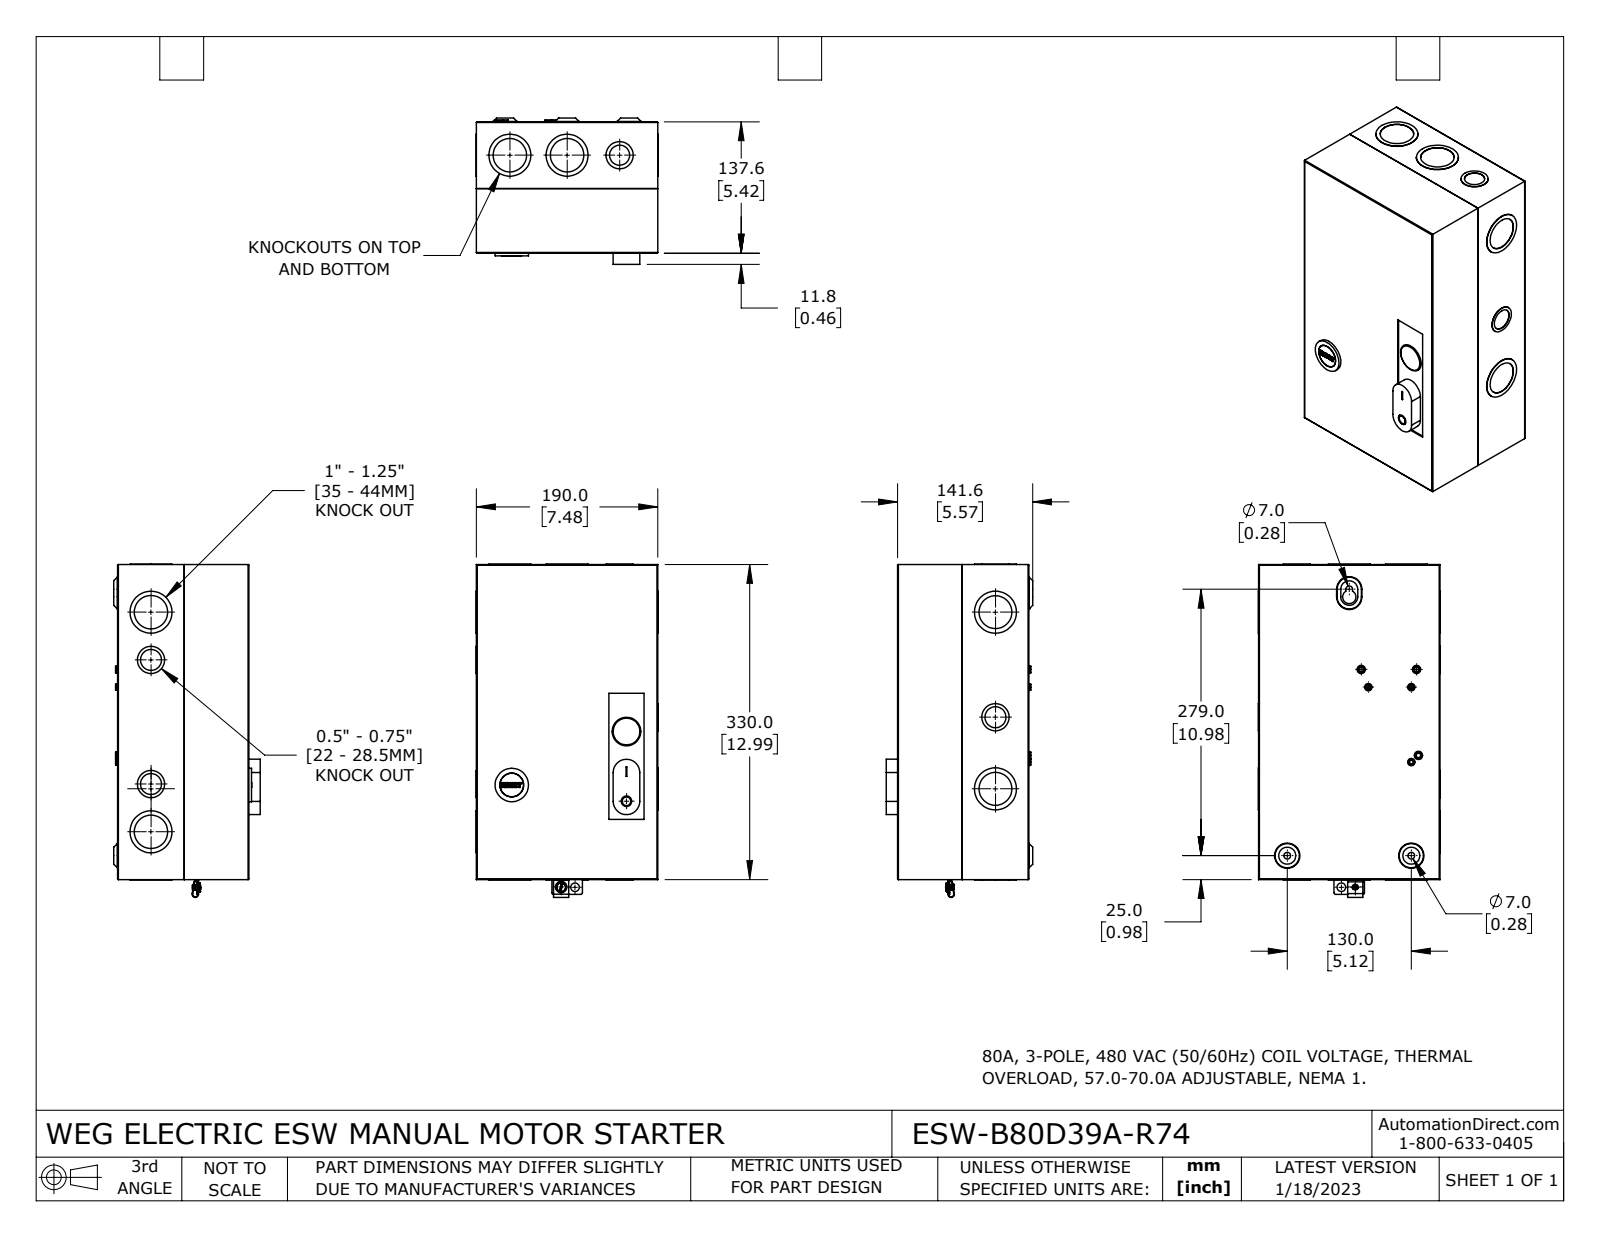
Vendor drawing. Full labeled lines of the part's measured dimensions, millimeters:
Part name (STEP PRODUCT): ESW-B80D39A-R74
STEP written by: SolidWorks 2021 (CONFIG_CONTROL_DESIGN)
Units: millimetres
Bodies: 7 solids, 435 faces (161 planar, 221 cylindrical, 53 other)
Overall size (bounding box): 349 × 190.6 × 153.4
Volume: 402 800 mm³ · Surface area: 604 300 mm²
Round holes (diameter × count): ⌀35 ×4, ⌀3.7 ×3, ⌀4.6 ×3, ⌀7 ×2, ⌀22 ×2, ⌀22.5 ×2, ⌀34.5 ×2, ⌀6.5 ×1, ⌀7.1 ×1, ⌀9 ×1, ⌀11 ×1, ⌀11.9 ×1
Round bosses / shafts (diameter × count): ⌀44 ×4, ⌀28.5 ×3, ⌀7.1 ×3, ⌀6.1 ×3, ⌀44 ×2, ⌀35 ×1, ⌀30.3 ×1, ⌀29.2 ×1
Partial cylindrical surfaces — rounded edges, fillets, slot ends (radius × count): R0.1 ×34, R0.8 ×8, R2 ×3, R3.5 ×3, R1.5 ×2, R1.9 ×2, R2.7 ×2, R3.1 ×2
Main face-to-face distances: 1.2, 136.4, 188.8, 135.2, 137.6, 328.8, 187.6, 190, 1.8, 327.6
Hole centre spacings: 14.5, 45, 50, 58, 60, 130, 180, 278.7
